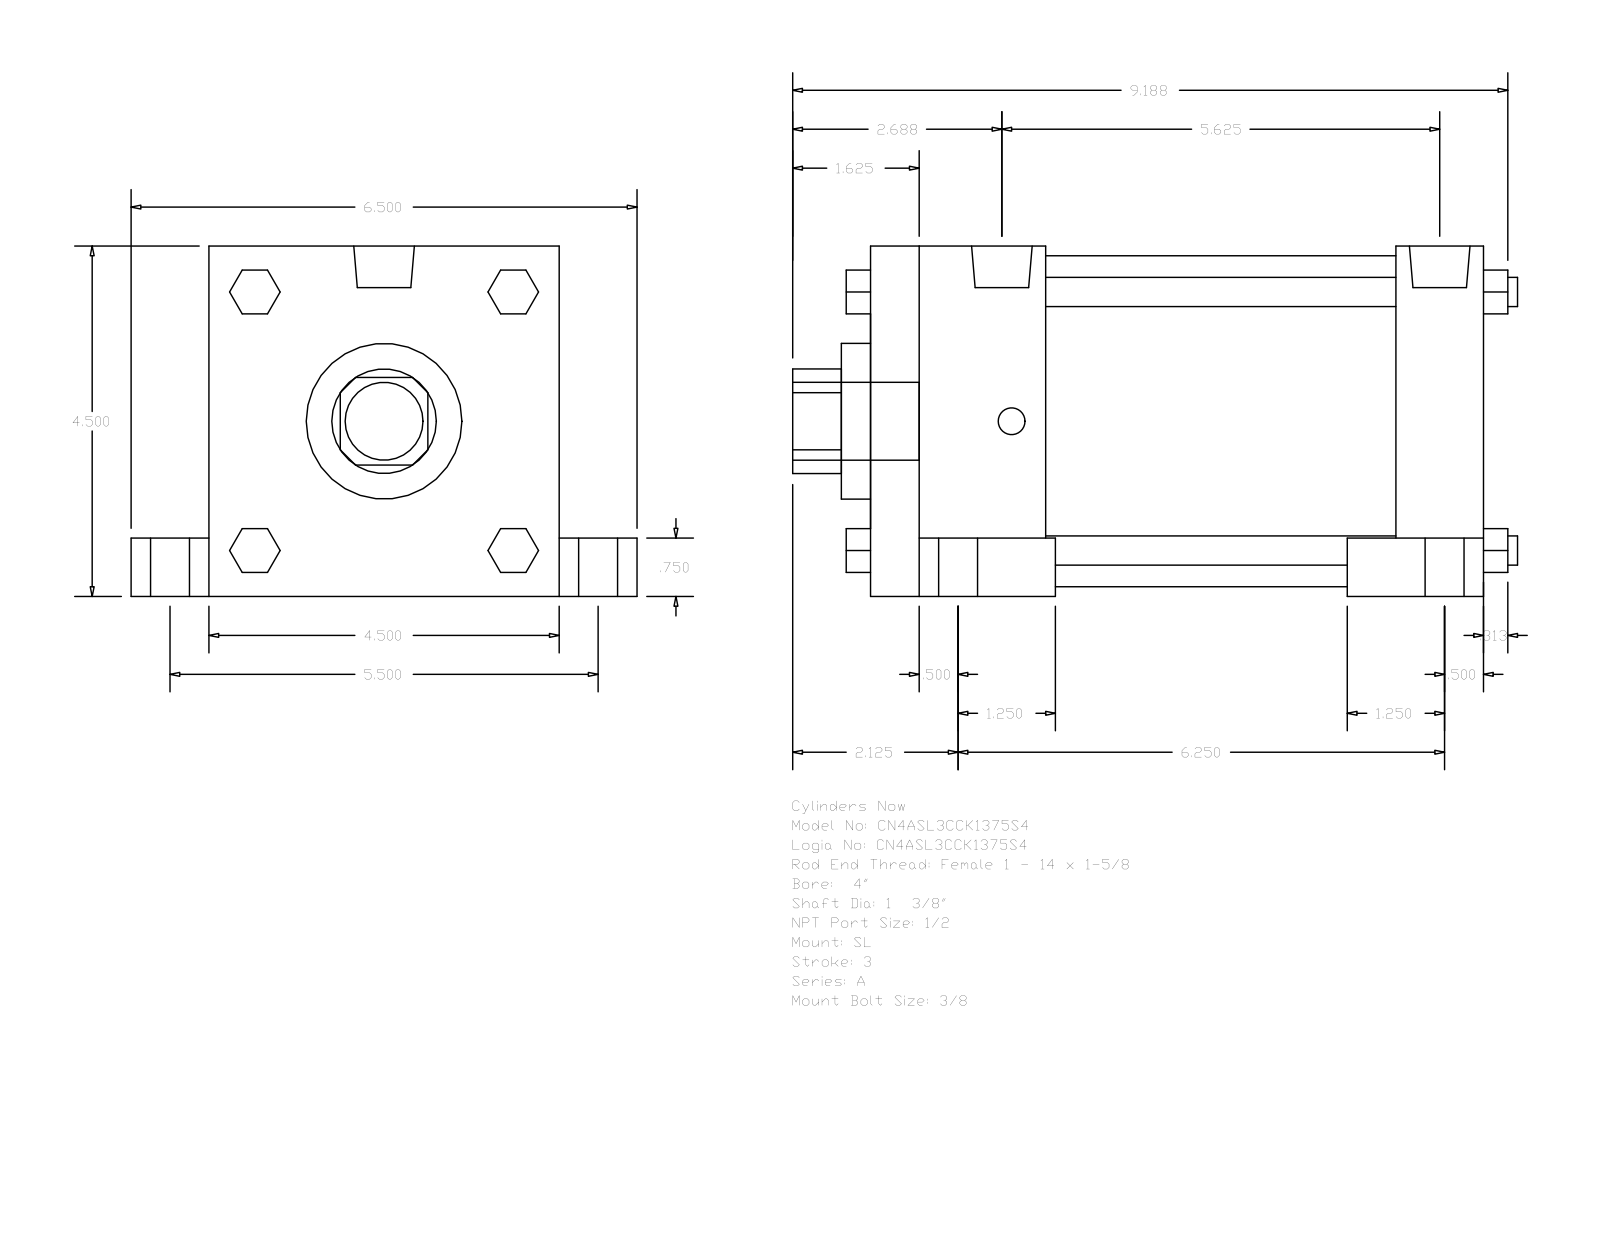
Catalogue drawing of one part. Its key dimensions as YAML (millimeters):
part_name: "A_SL__0400_1.375"
step_written_by: "GSSL Pune (CONFIG_CONTROL_DESIGN)"
units: millimeters
bodies: {solids: 0, faces: 150, planar: 114, cylindrical: 36, other: 0}
overall_size: [236.54, 165.1, 114.3]
round_holes:
  - {diameter: 34.92, count: 1}
  - {diameter: 50.8, count: 1}
  - {diameter: 107.95, count: 1}
round_bosses_or_shafts:
  - {diameter: 19.05, count: 4}
  - {diameter: 12.7, count: 4}
  - {diameter: 9.53, count: 4}
  - {diameter: 8.73, count: 4}
  - {diameter: 19.77, count: 2}
  - {diameter: 25.4, count: 1}
partial_cylinders:
  - {radius: 17.06, count: 1}
face_to_face_distances: [114.3, 200.03, 139.7, 95.25, 28.58, 25.4, 57.15, 142.88, 171.45, 19.05]
